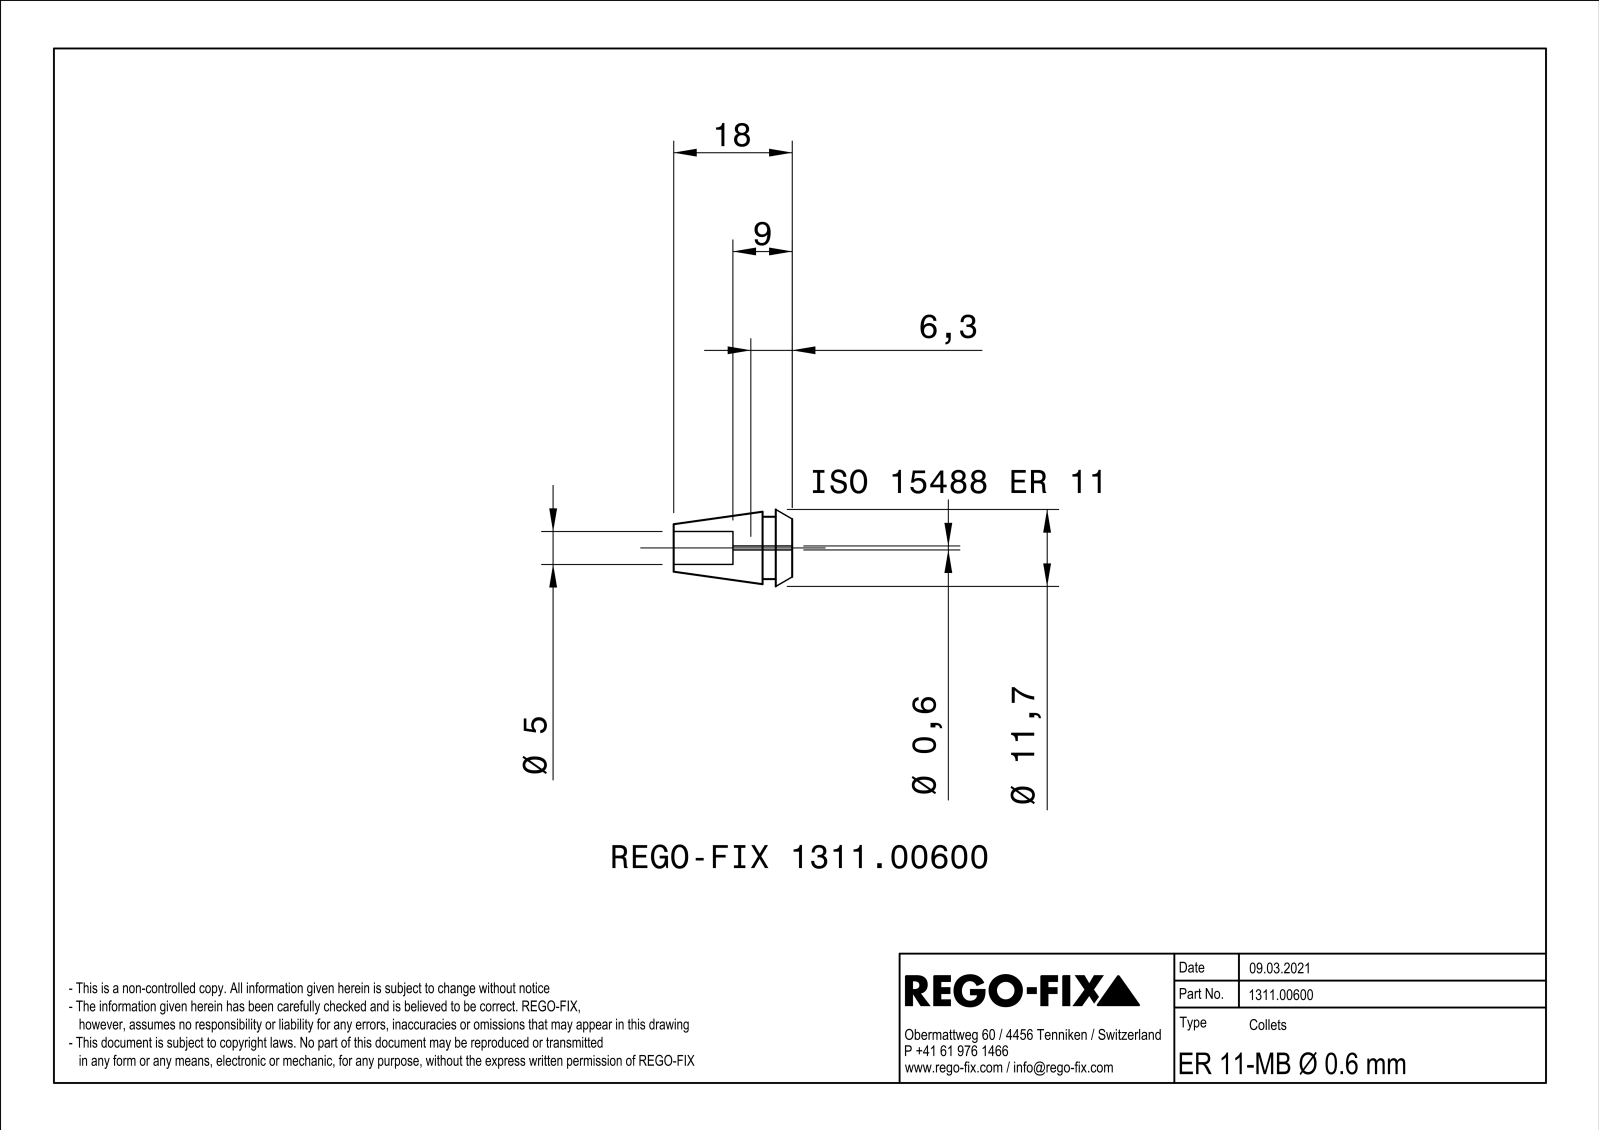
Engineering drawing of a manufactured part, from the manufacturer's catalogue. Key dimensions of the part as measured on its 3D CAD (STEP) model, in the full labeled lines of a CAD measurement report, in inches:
Part name (STEP PRODUCT): NOCUT
STEP written by: SIEMENS PLM Software Solid Edge ST10 (AUTOMOTIVE_DESIGN)
Units: inches
Bodies: 1 solid, 91 faces (26 planar, 19 cylindrical, 46 other)
Overall size (bounding box): 0.709 × 0.439 × 0.438
Volume: 0.055 in³ · Surface area: 1.868 in²
Round holes (diameter × count): ⌀0.059 ×3, ⌀0.197 ×1
Round bosses / shafts (diameter × count): ⌀0.374 ×1
Partial cylindrical surfaces — rounded edges, fillets, slot ends (radius × count): R0.984 ×3, R0.012 ×1
Main face-to-face distances: 0.031, 0.02, 0.177, 0.354, 0.098, 0.709, 0.61, 0.079, 0.531, 0.256
Hole centre spacings: 0.067, 0.116
